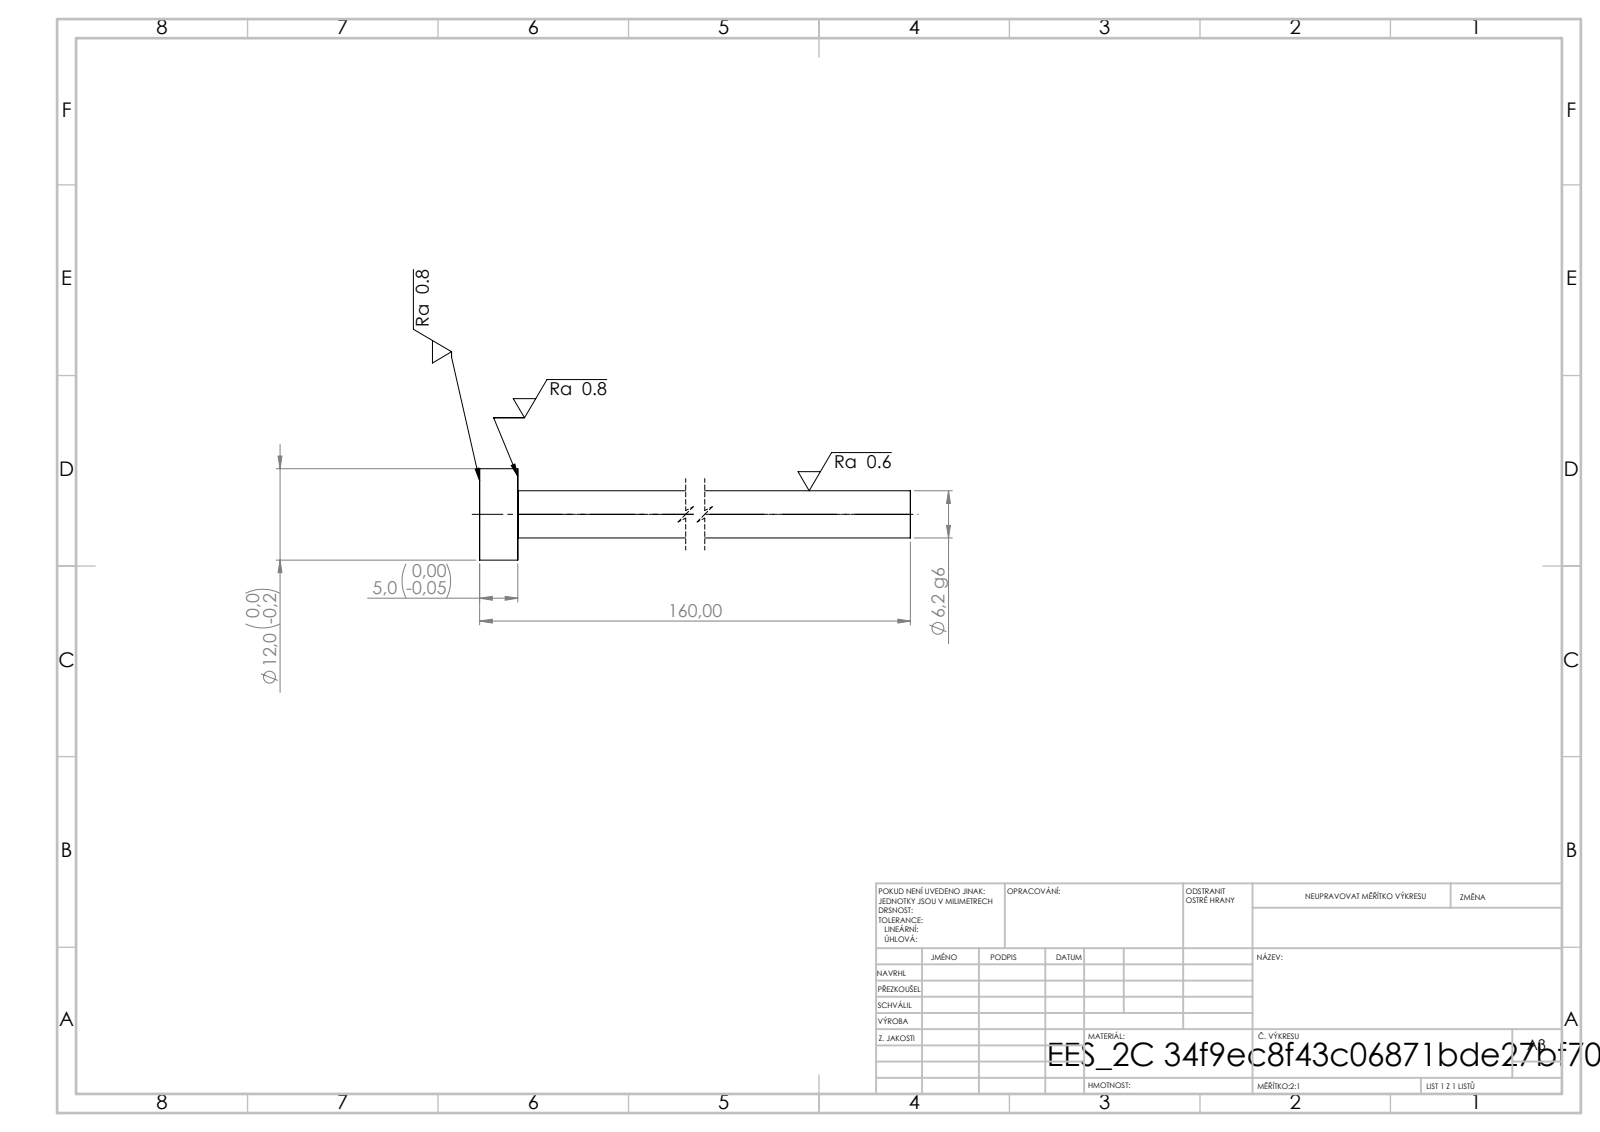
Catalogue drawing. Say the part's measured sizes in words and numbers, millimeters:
Its 3-D file was written by "SolidWorks 2019 (CONFIG_CONTROL_DESIGN)". It is 1 solid with 7 faces: 3 planar, 4 cylindrical and 0 other. Overall it measures 160 by 12 by 12 millimeters. Its volume is 5 245 cubic millimeters and its surface area 3 434 square millimeters. Round bosses or shafts: 1 of diameter 12, 1 of diameter 6.2. The main face-to-face distances are 5, 160, 155.
